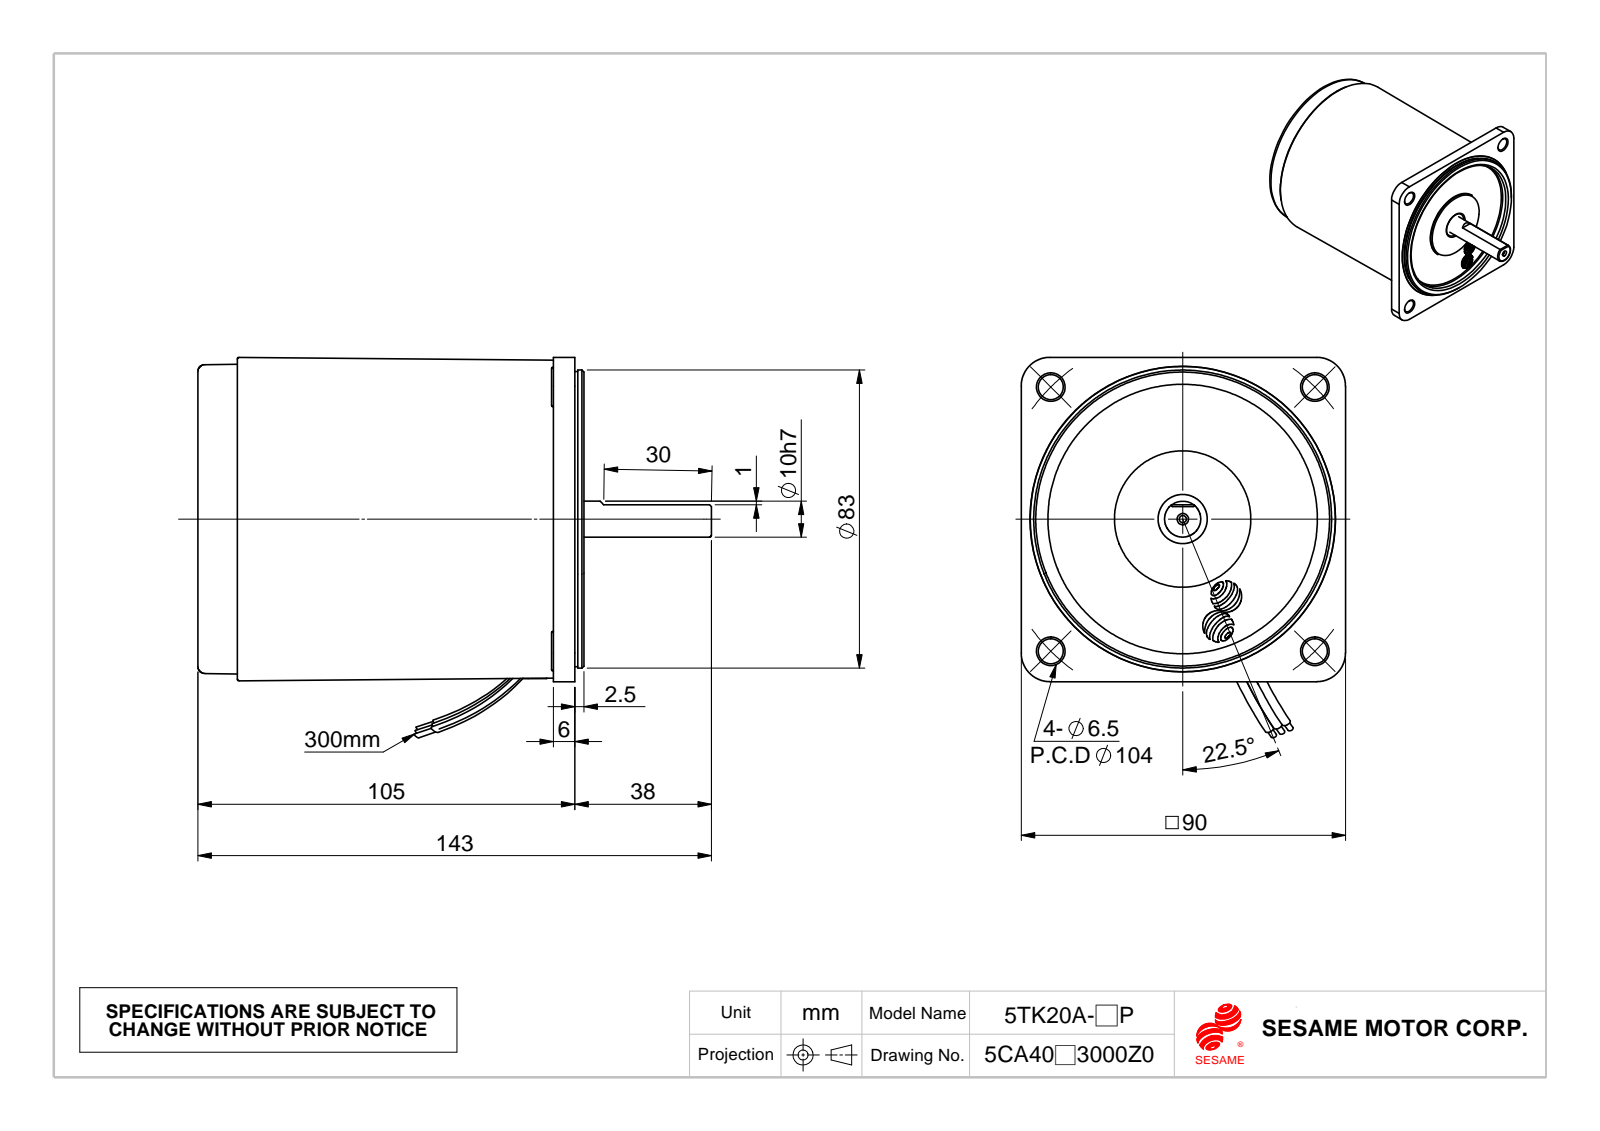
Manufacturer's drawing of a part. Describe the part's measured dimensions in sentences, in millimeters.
The part is named "M540; 40A; 線扣". Its 3-D file was written by "SolidWorks 2010 (CONFIG_CONTROL_DESIGN)". It is 7 solids with 364 faces: 75 planar, 195 cylindrical and 94 other. Overall it measures 143 by 105.88 by 90.3 millimeters. Its volume is 664 402 cubic millimeters and its surface area 66 054 square millimeters. Round holes: 4 of diameter 7, 1 of diameter 2, 1 of diameter 2.5, 1 of diameter 7.2, 1 of diameter 9.5, 1 of diameter 13.7, 1 of diameter 26, 1 of diameter 58.1, 1 of diameter 75, 1 of diameter 84.4, 1 of diameter 85. Round bosses or shafts: 1 of diameter 84.22, 1 of diameter 84.15, 1 of diameter 83, 1 of diameter 82.2, 1 of diameter 38, 1 of diameter 10, 1 of diameter 9.3. Partial cylindrical surfaces (rounded edges, fillets, slot ends): 8 of radius 0.25, 8 of radius 0.78, 8 of radius 1.5, 8 of radius 1.66, 8 of radius 2.92, 4 of radius 0.2, 4 of radius 0.58, 4 of radius 2.58. The main face-to-face distances are 1, 102.5, 0.9, 103.5, 2.5, 101.5, 102.4, 103.4, 1.5, 105. The hole center spacings are 52, 73.54, 104.
